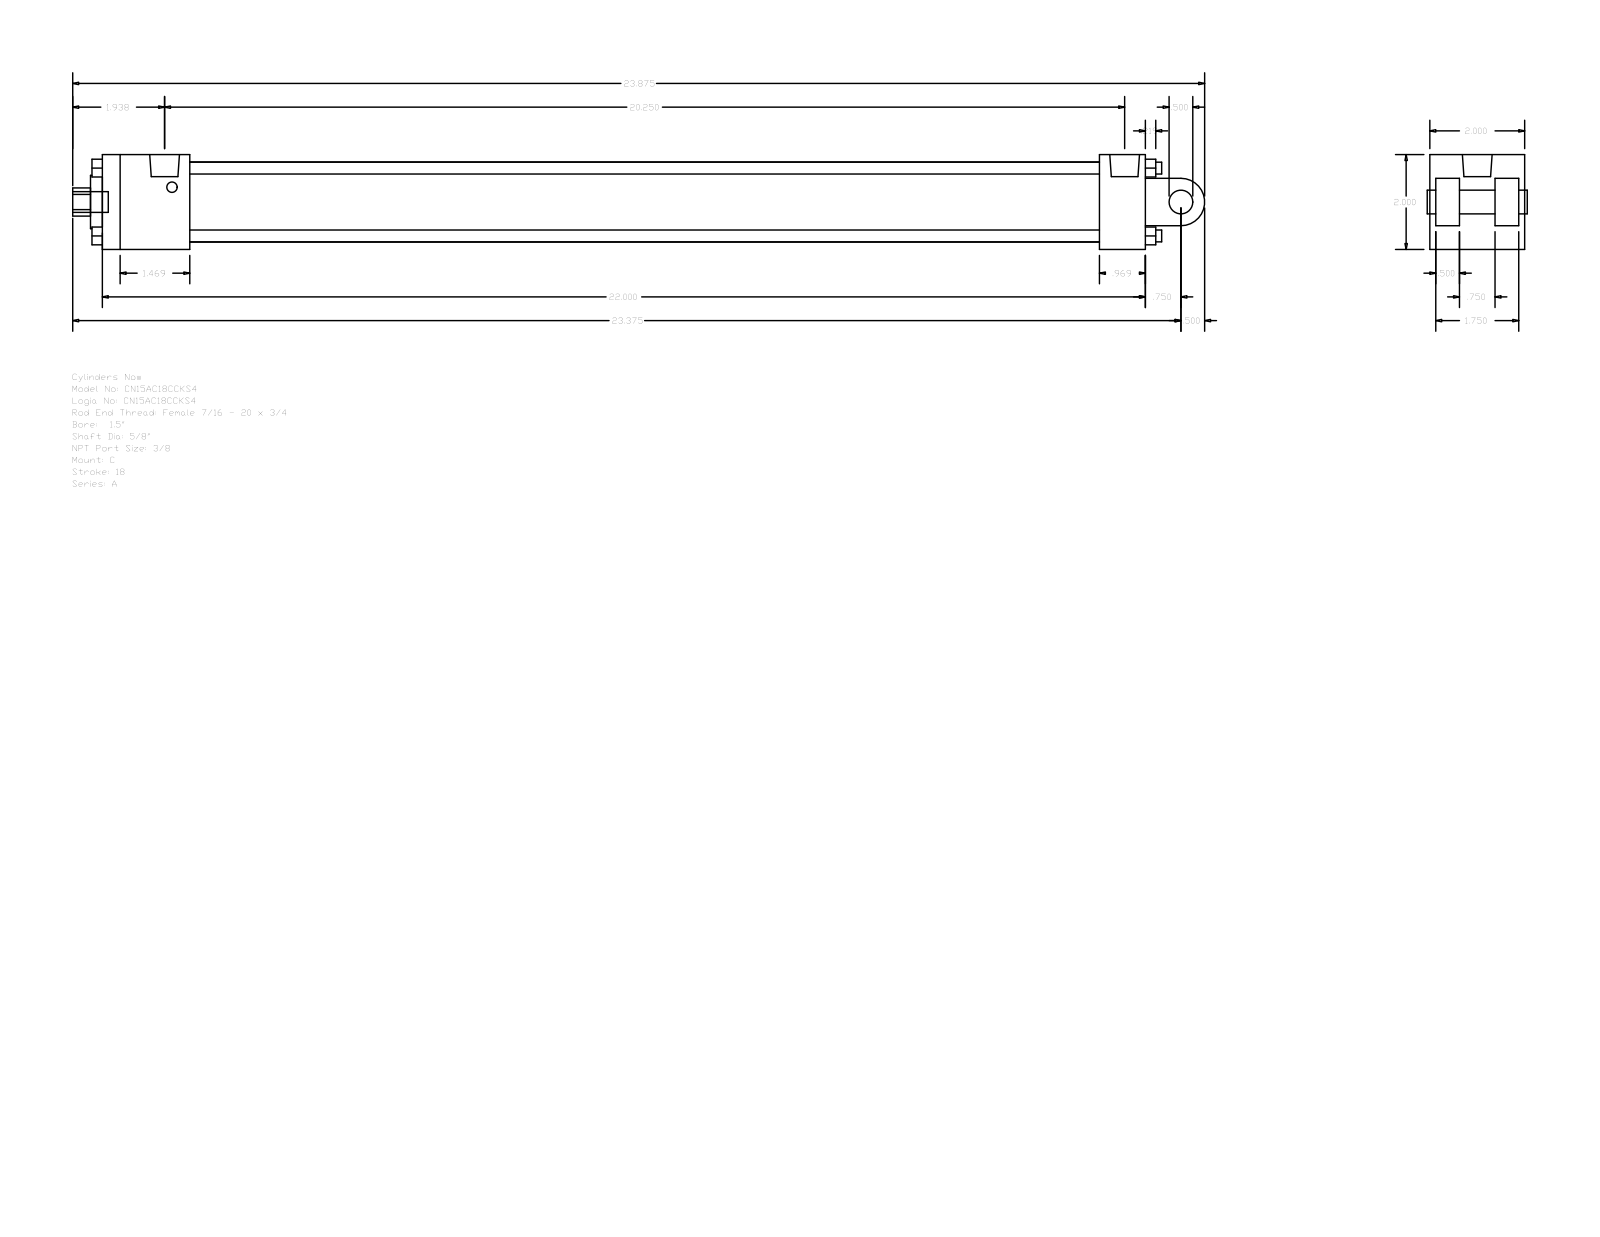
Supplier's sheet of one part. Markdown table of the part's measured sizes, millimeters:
| quantity | value |
| --- | --- |
| part name | A_C__0150_0.625 |
| STEP written by | GSSL Pune (CONFIG_CONTROL_DESIGN) |
| units | millimeters |
| bodies | 0 solids, 135 faces (102 planar, 33 cylindrical, 0 other) |
| overall size | 606.42 × 50.8 × 50.8 |
| round holes (diameter × count) | 5.56 × 2, 15.88 × 1, 15.93 × 1, 28.57 × 1, 42.93 × 1 |
| round bosses / shafts (diameter × count) | 6.35 × 4, 5.56 × 2, 15.93 × 1, 12.7 × 1, 11.11 × 1 |
| partial cylindrical surfaces (radius × count) | 7.54 × 1, 12.7 × 1 |
| main face-to-face distances | 50.8, 12.7, 558.79, 3.17, 47.63, 15.87, 34.93, 31.76, 534.19, 24.6 |
| hole center spacings | 3.97 |
